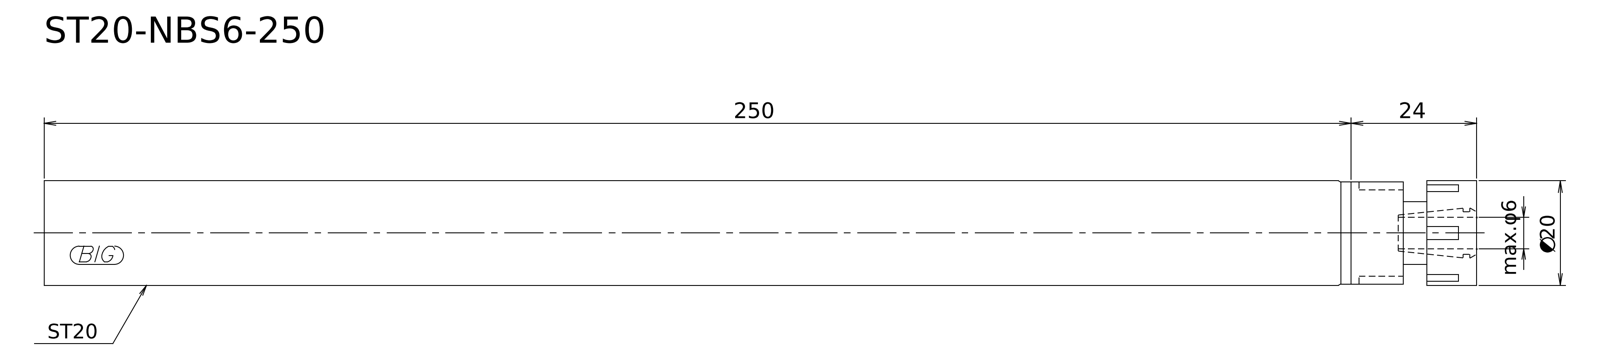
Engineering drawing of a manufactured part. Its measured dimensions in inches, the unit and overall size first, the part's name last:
Units: inches
Overall size (bounding box): 10.787 × 0.787 × 0.787
Round bosses / shafts (diameter × count): ⌀0.787 ×1, ⌀0.768 ×1, ⌀0.472 ×1
Main face-to-face distances: 10.787, 0.374, 10.413, 0.551, 0.177, 10.236, 1.026, 0.652, 0.474, 9.762
Volume: 5.186 in³ · Surface area: 28.08 in²
Bodies: 1 solid, 9 faces (5 planar, 4 cylindrical, 0 other)
STEP written by: Kubotek KeyCreator V8.5.1 (14335) (CONFIG_CONTROL_DESIGN)
